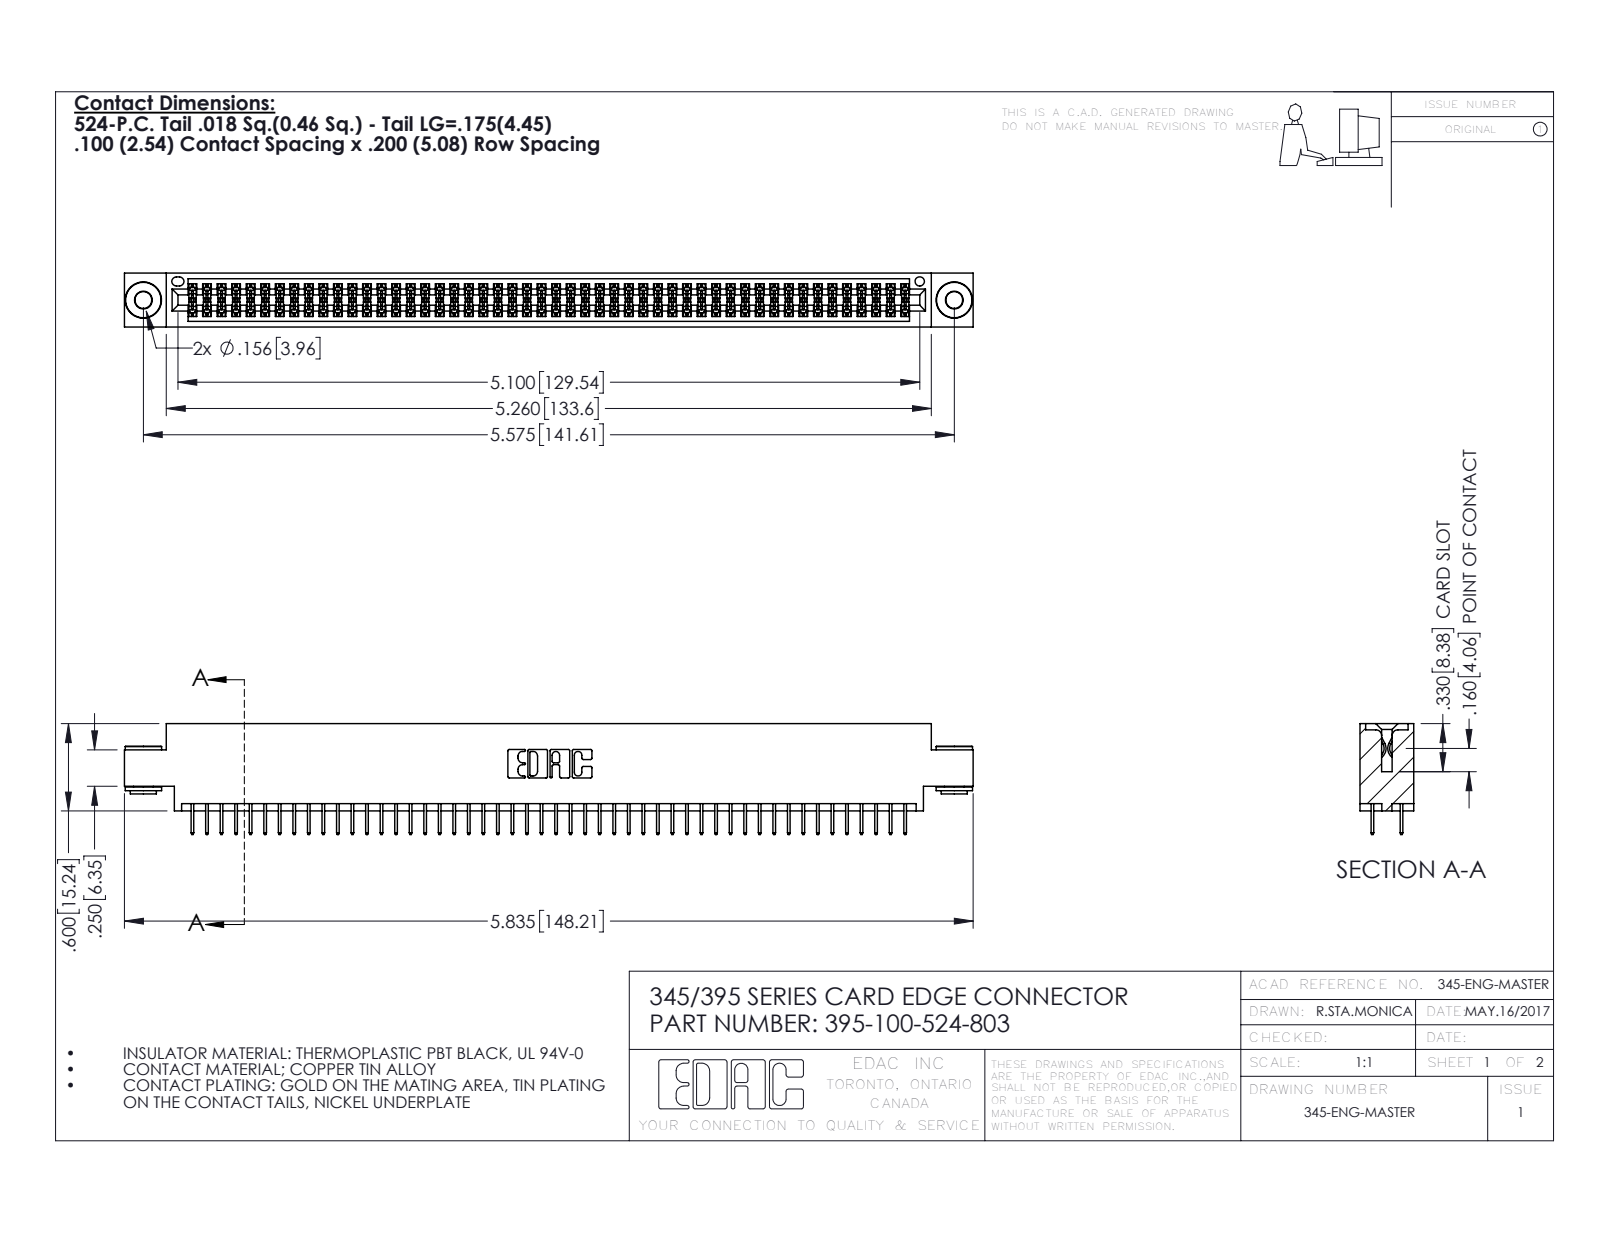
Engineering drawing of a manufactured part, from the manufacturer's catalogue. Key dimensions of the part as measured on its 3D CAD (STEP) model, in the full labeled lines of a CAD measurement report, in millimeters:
Part name (STEP PRODUCT): 345-250-002_345-250-002-102; 345-292-001_345-293-124; 345 Part_0.170 Offset - 0.156 Dia-TH; 395-100-524-803
STEP written by: SolidWorks 2016 (CONFIG_CONTROL_DESIGN)
Units: millimetres
Bodies: 103 solids, 5568 faces (3994 planar, 1566 cylindrical, 8 other)
Overall size (bounding box): 148.2 × 19.4 × 9.4
Volume: 14 200 mm³ · Surface area: 21 140 mm²
Round holes (diameter × count): ⌀2.9 ×2, ⌀4 ×2, ⌀1.6 ×1
Round bosses / shafts (diameter × count): ⌀6.4 ×2, ⌀4.6 ×2, ⌀3.5 ×2
Partial cylindrical surfaces — rounded edges, fillets, slot ends (radius × count): R0.2 ×150, R0.3 ×22, R0.2 ×6, R0.8 ×6, R0.7 ×3, R0.4 ×2, R0.5 ×2, R0.6 ×2
Main face-to-face distances: 1.8, 7.6, 9.4, 5.1, 2.5, 6.9, 0.6, 5.7, 4.4, 1.8
Hole centre spacings: 6.9, 135.6, 141.6
